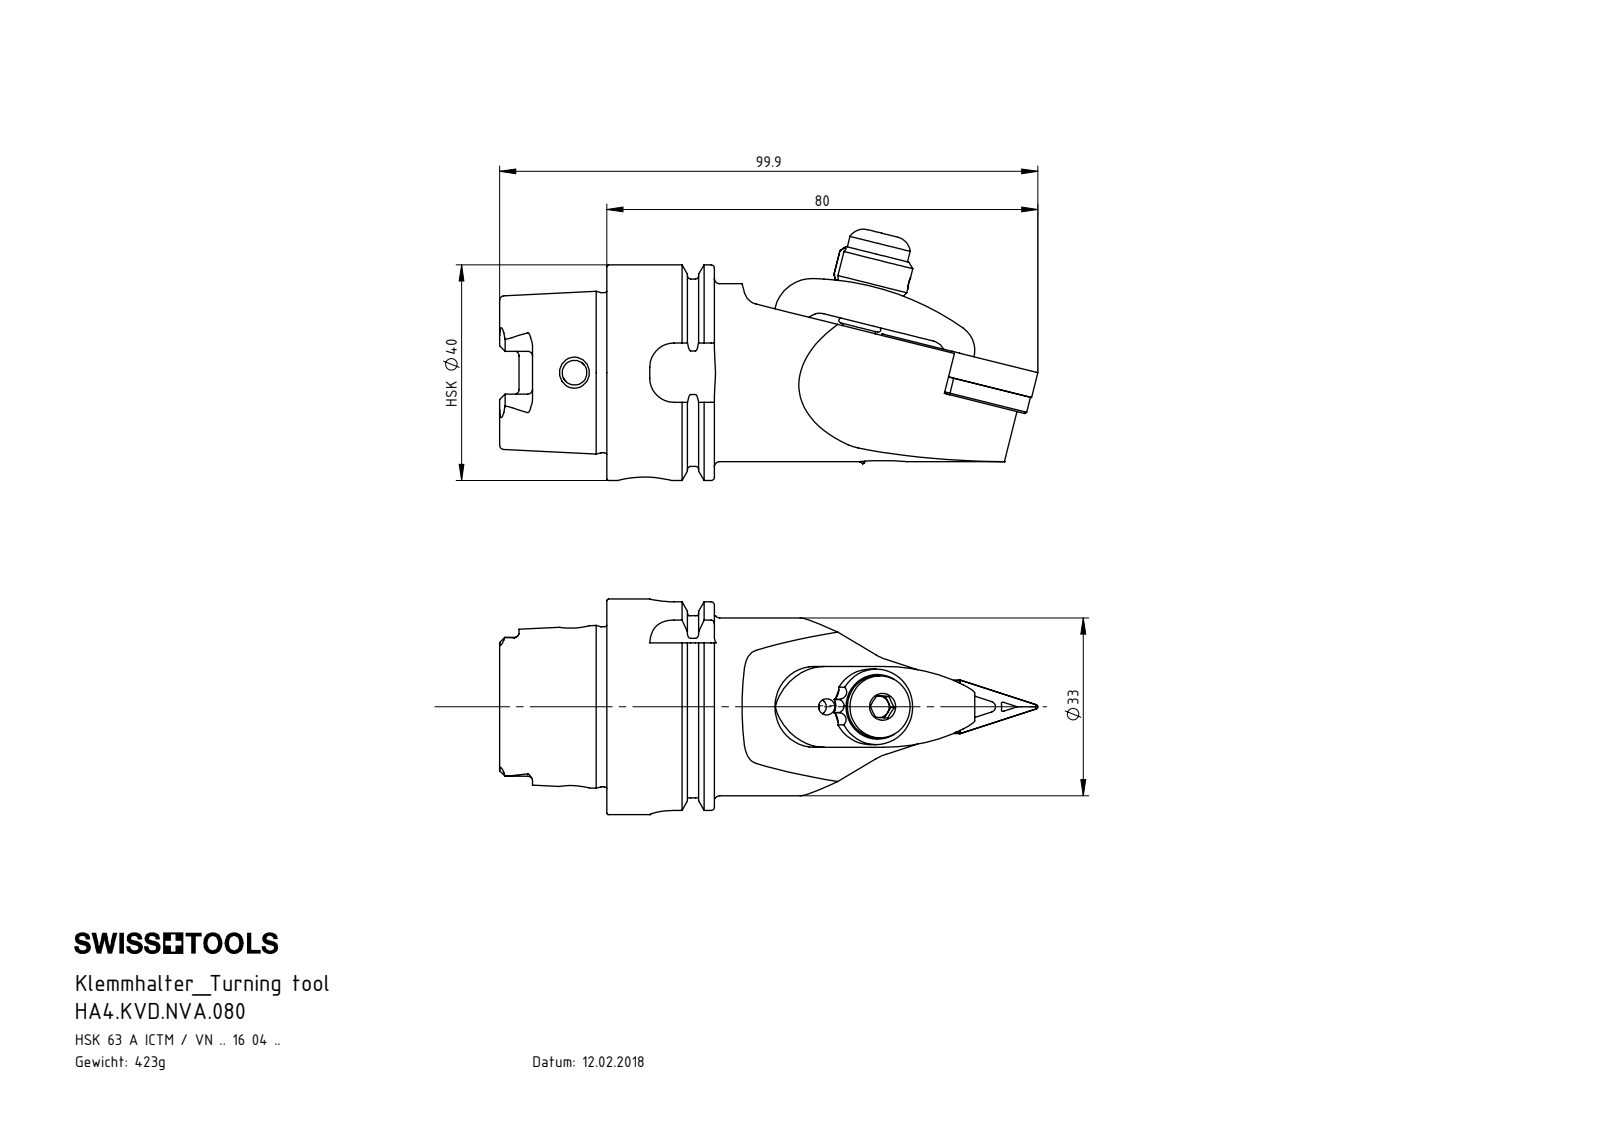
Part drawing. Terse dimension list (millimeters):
name: WCC-ER3.102.029_C; WCC-ER5.102.012_B; WVD-ER2.101.003_A; WCC-ER5.102.005_A (+6 more)
written by: SolidWorks 2017 (AUTOMOTIVE_DESIGN)
unit: mm
bodies: 10 solids, 458 faces (122 planar, 151 cylindrical, 185 other)
size: 99.9 × 46.63 × 40
volume: 53 367 mm³; area: 19 493 mm²
holes: 3× ⌀2, 3× ⌀5, 2× ⌀7, 1× ⌀3, 1× ⌀3.3, 1× ⌀3.8, 1× ⌀4, 1× ⌀4.2, 1× ⌀4.6, 1× ⌀4.95, 1× ⌀6.2, 1× ⌀6.9
bosses: 2× ⌀4, 1× ⌀40, 1× ⌀34.75, 1× ⌀33, 1× ⌀29.71, 1× ⌀14, 1× ⌀11.5, 1× ⌀6.8
rounds: 6× R0.34, 6× R0.59, 6× R0.9, 4× R0.4, 4× R1.88, 4× R4.5, 3× R1.5, 3× R3
face distances: 8.94, 4.46, 5.76, 1.3, 3.18, 7.64, 9.53, 0.59, 7.95, 12
hole spacings: 19.31, 8.02, 19.12, 8.2, 19.3, 27.32, 27.33
